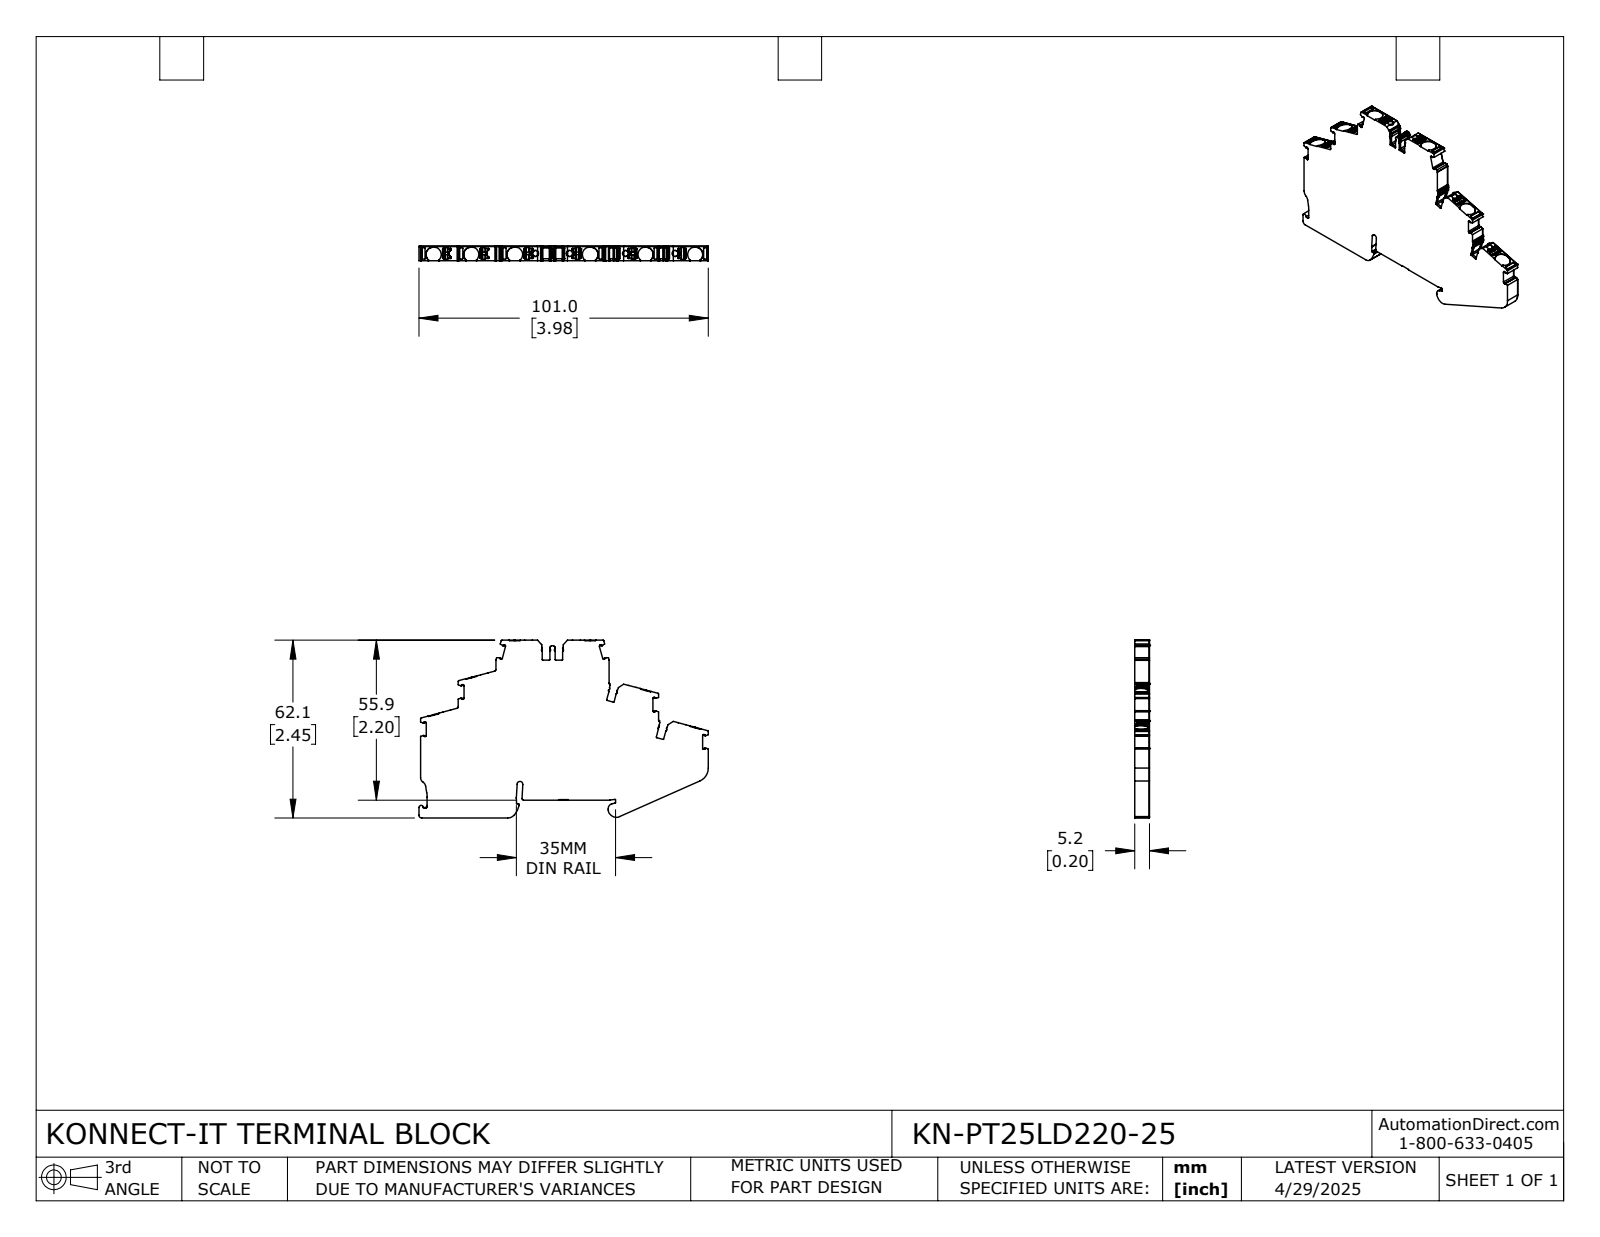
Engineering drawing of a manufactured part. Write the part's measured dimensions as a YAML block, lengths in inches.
part_name: "KN-PT25LD220-25"
step_written_by: "SolidWorks 2024 (CONFIG_CONTROL_DESIGN)"
units: inches
bodies: {solids: 1, faces: 1212, planar: 579, cylindrical: 528, other: 105}
overall_size: [3.977, 2.445, 0.203]
volume: 1.354
surface_area: 16.76
round_holes:
  - {diameter: 0.083, count: 4}
partial_cylinders:
  - {radius: 0.008, count: 128}
  - {radius: 0.004, count: 49}
  - {radius: 0.012, count: 47}
  - {radius: 0.02, count: 26}
  - {radius: 0.006, count: 24}
  - {radius: 0.016, count: 17}
  - {radius: 0.024, count: 14}
  - {radius: 0.006, count: 12}
face_to_face_distances: [0.203, 0.246, 0.079, 2.191, 2.437, 0.319, 0.682, 0.519, 2.445, 2.199]
hole_center_spacings: [0.466, 0.792]
